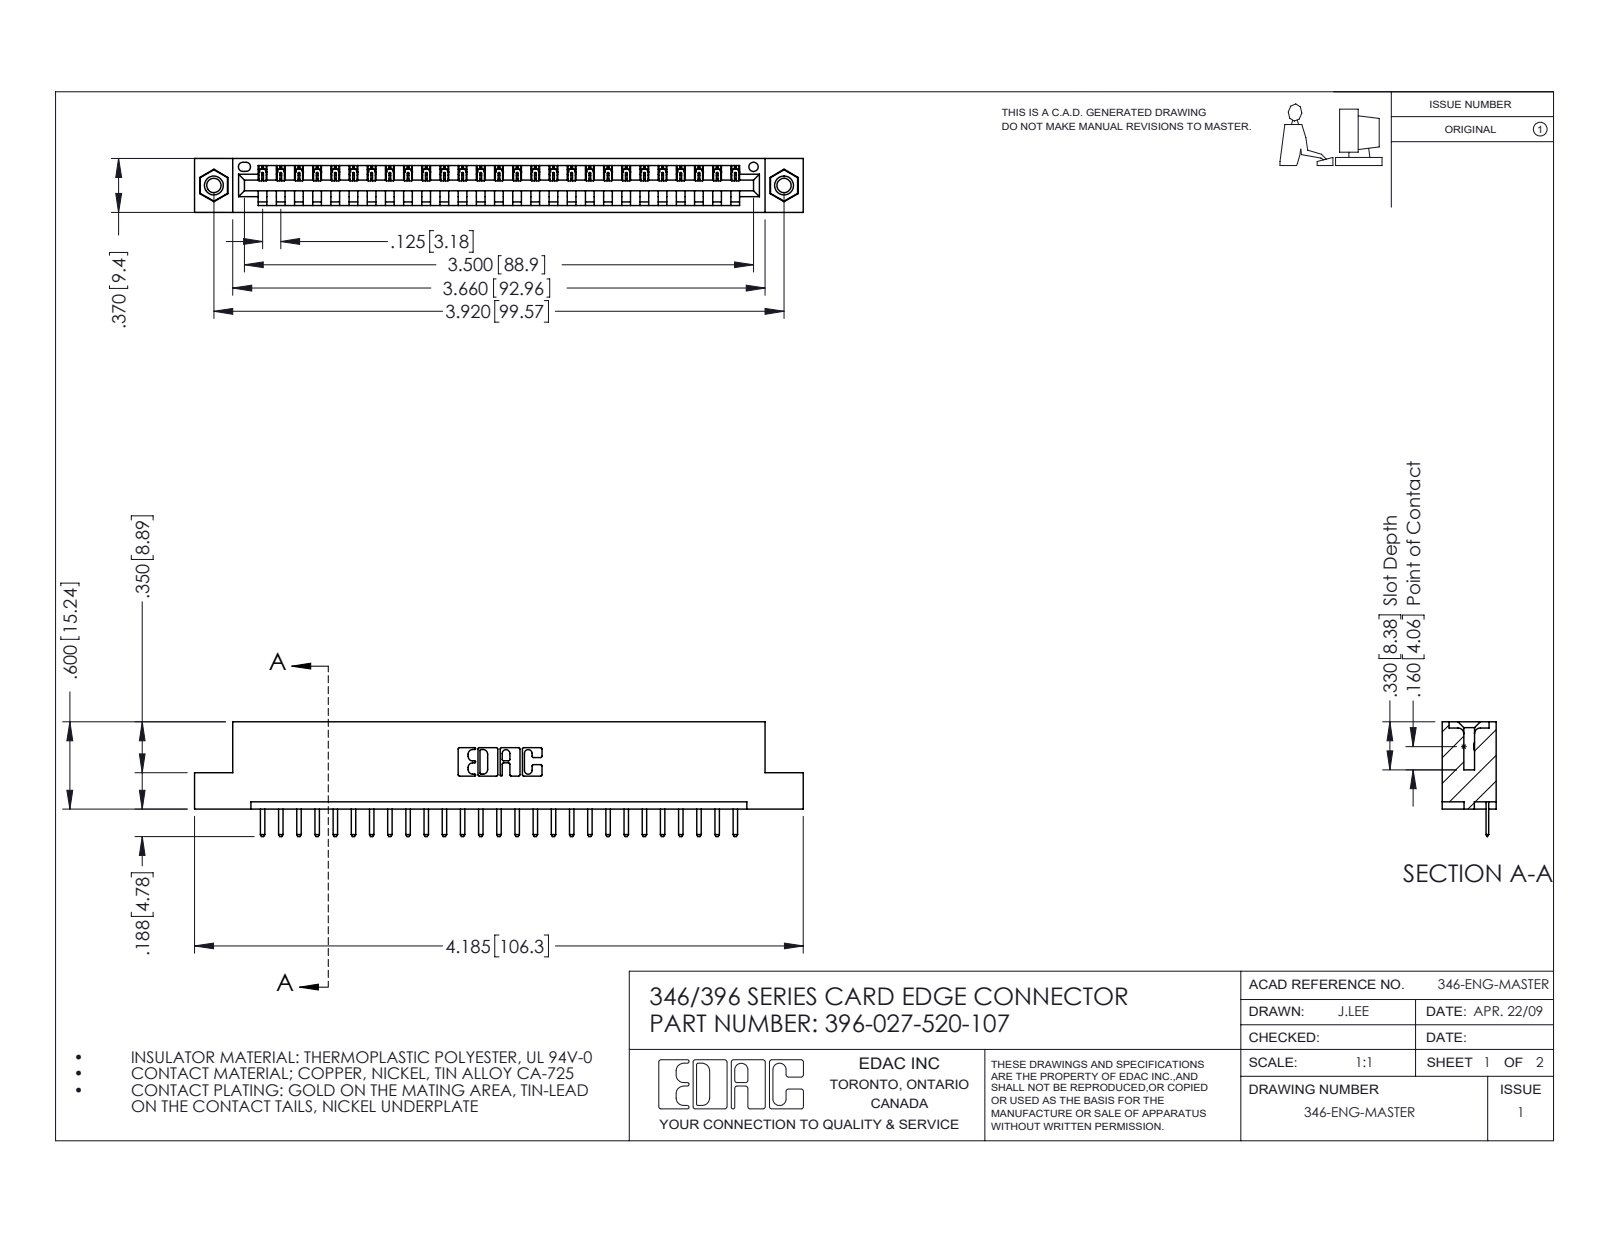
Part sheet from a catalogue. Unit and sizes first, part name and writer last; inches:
Units: inches
Overall size (bounding box): 4.185 × 0.788 × 0.37
Round holes (diameter × count): ⌀0.098 ×2, ⌀0.125 ×2, ⌀0.156 ×2, ⌀0.064 ×1
Round bosses / shafts (diameter × count): ⌀0.155 ×2
Partial cylindrical surfaces — rounded edges, fillets, slot ends (radius × count): R0.01 ×56, R0.006 ×54, R0.01 ×22, R0.007 ×6, R0.031 ×6, R0.026 ×3, R0.031 ×2, R0.04 ×2
Main face-to-face distances: 0.048, 0.322, 0.37, 0.25, 0.148, 0.222, 0.1, 0.174, 0.072, 0.298
Hole centre spacings: 0.246, 3.712, 3.92
Volume: 0.609 in³ · Surface area: 18.74 in²
Bodies: 30 solids, 1856 faces (1242 planar, 598 cylindrical, 16 other)
Part name (STEP PRODUCT): 346 Part_Flush Mounting Lugs - 0.156 Dia-TI; 396-027-520-107; 345-292-001_345-293-120; 345-250-001_345-250-005-103
STEP written by: SolidWorks 2016 (CONFIG_CONTROL_DESIGN)
